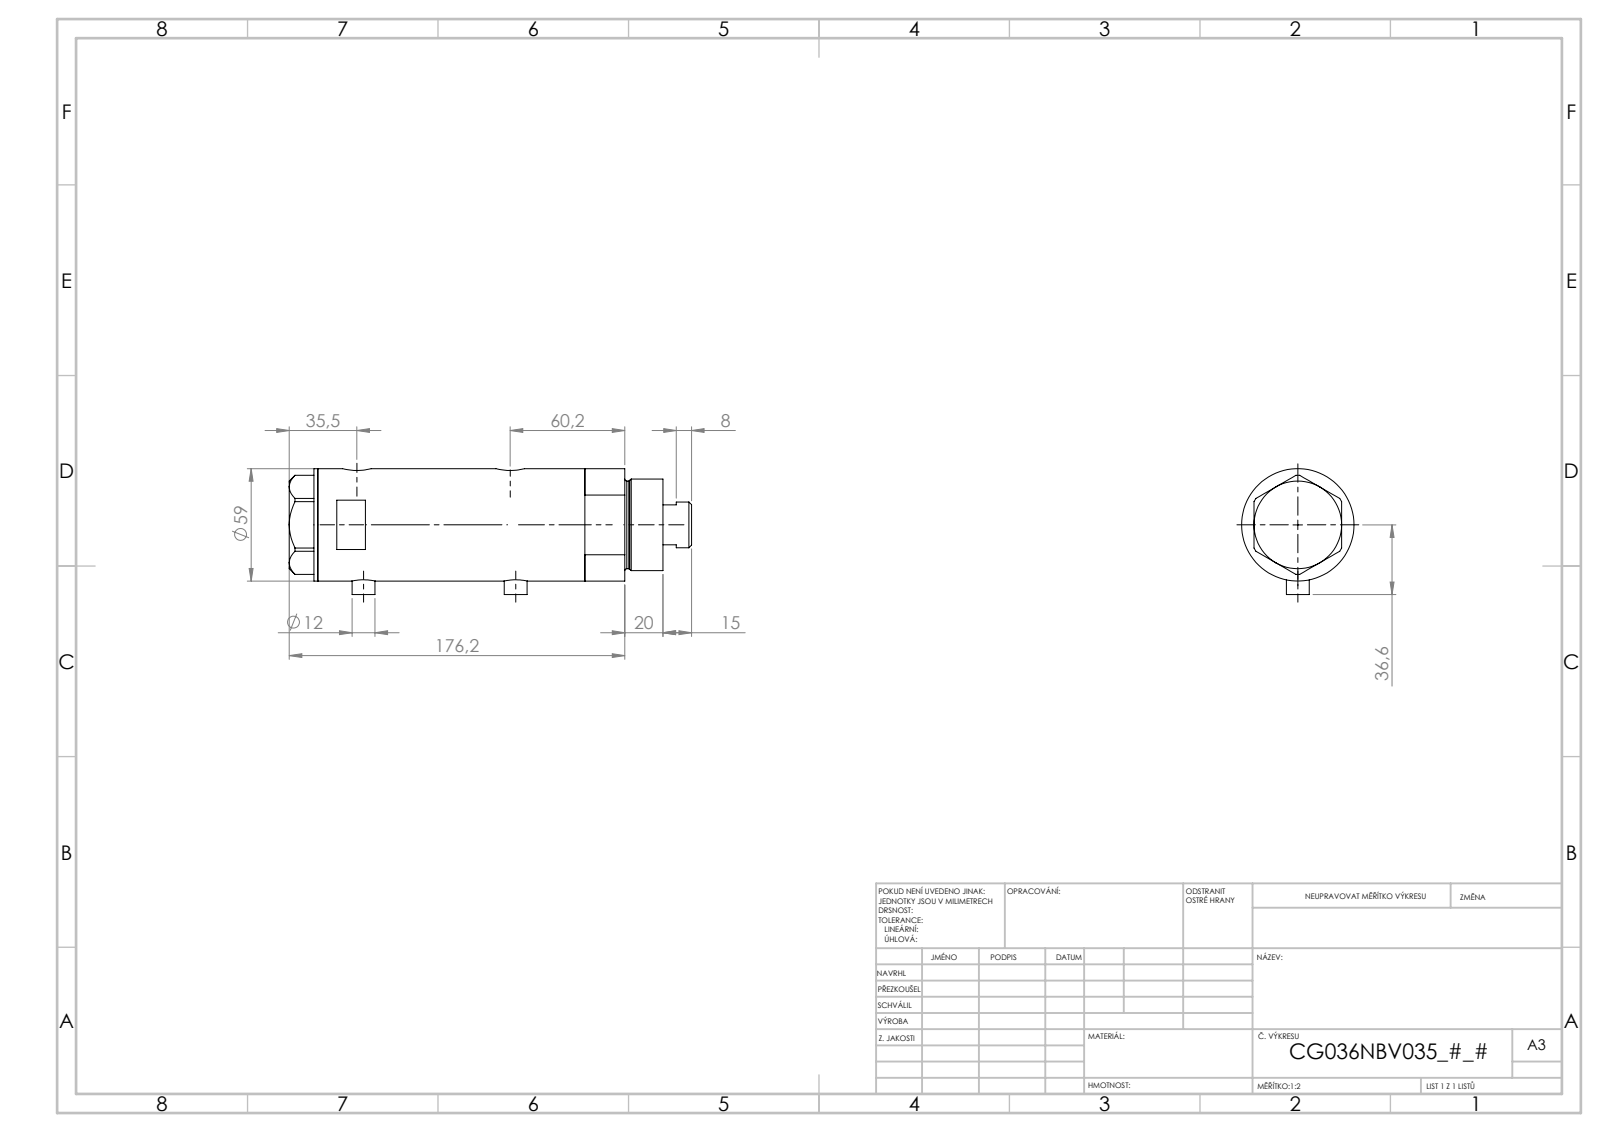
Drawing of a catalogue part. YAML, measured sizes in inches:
part_name: "V270CG_BACK; V270CG_FRONT; V270CG_MIDDLE; V270CG_VC"
step_written_by: "SolidWorks 2019 (CONFIG_CONTROL_DESIGN)"
units: inches
bodies: {solids: 4, faces: 126, planar: 53, cylindrical: 53, other: 20}
overall_size: [7.812, 2.366, 2.323]
volume: 27.36
surface_area: 147.4
round_holes:
  - {diameter: 0.197, count: 2}
  - {diameter: 0.383, count: 2}
  - {diameter: 0.492, count: 2}
  - {diameter: 0.591, count: 2}
  - {diameter: 0.335, count: 1}
  - {diameter: 0.984, count: 1}
  - {diameter: 1.043, count: 1}
  - {diameter: 1.417, count: 1}
  - {diameter: 1.575, count: 1}
  - {diameter: 2.047, count: 1}
round_bosses_or_shafts:
  - {diameter: 0.472, count: 2}
  - {diameter: 2.323, count: 1}
  - {diameter: 1.89, count: 1}
  - {diameter: 1.811, count: 1}
  - {diameter: 0.945, count: 1}
face_to_face_distances: [3.635, 0.925, 2.71, 0.591, 1.516, 4.226, 7.221, 6.631, 5.706, 2.995]
hole_center_spacings: [0.114, 0.138, 2.644, 2.758, 2.781, 2.896, 0.114, 0.115]
